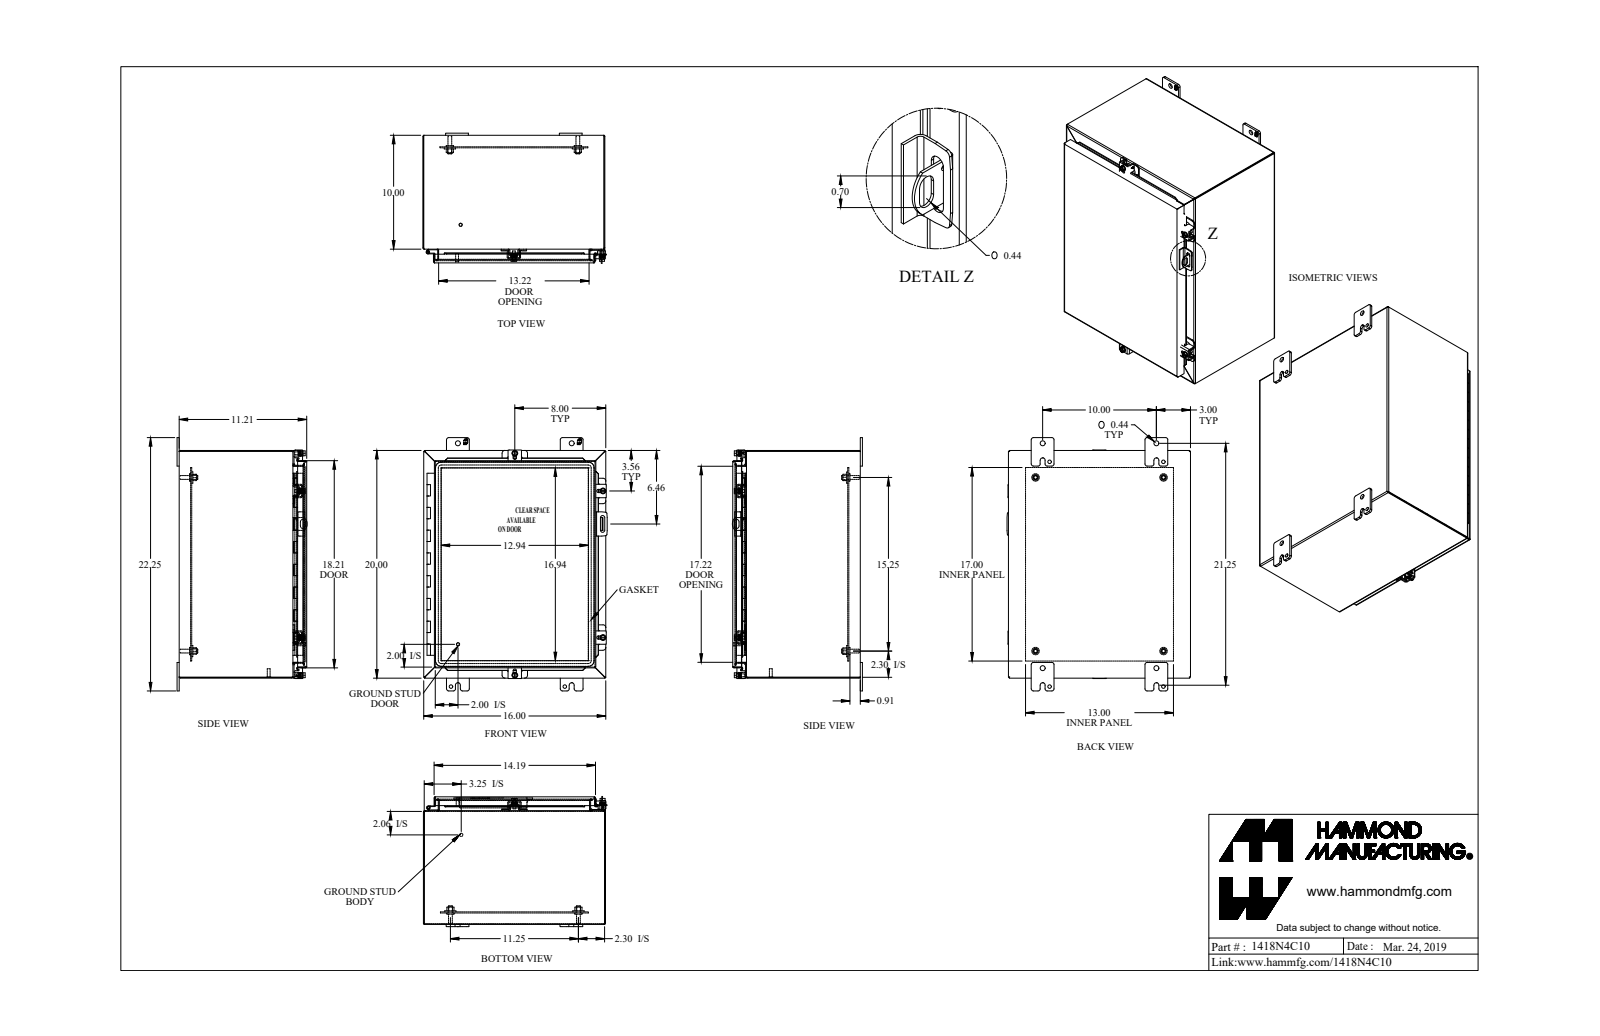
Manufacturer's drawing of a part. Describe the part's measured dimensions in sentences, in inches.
The part is named "1418N4C10_Default". Its 3-D file was written by "SolidWorks 2019 (CONFIG_CONTROL_DESIGN)". It is 39 solids with 1366 faces: 833 planar, 449 cylindrical and 84 other. Overall it measures 22.25 by 16.125 by 11.437 inches. Its volume is 143.6 cubic inches and its surface area 3 803 square inches. Round holes: 4 of diameter 0.213, 4 of diameter 0.265, 4 of diameter 0.313, 4 of diameter 0.375, 4 of diameter 0.437, 4 of diameter 0.5, 2 of diameter 0.307, 2 of diameter 0.445, 1 of diameter 0.125, 1 of diameter 0.187. Round bosses or shafts: 4 of diameter 0.65, 4 of diameter 0.5, 4 of diameter 0.39, 4 of diameter 0.375, 4 of diameter 0.33, 4 of diameter 0.244, 2 of diameter 1, 2 of diameter 0.281. Partial cylindrical surfaces (rounded edges, fillets, slot ends): 26 of radius 0.188, 24 of radius 0.036, 24 of radius 0.108, 21 of radius 0.048, 21 of radius 0.143, 20 of radius 0.25, 8 of radius 0.045, 8 of radius 0.125. The main face-to-face distances are 0.072, 15.928, 19.928, 0.072, 11.066, 11.138, 0.937, 11.138, 11.21, 1.009. The hole center spacings are 18.951, 10, 15.25, 18.263, 2.434, 6.013, 11.041, 16.762.
